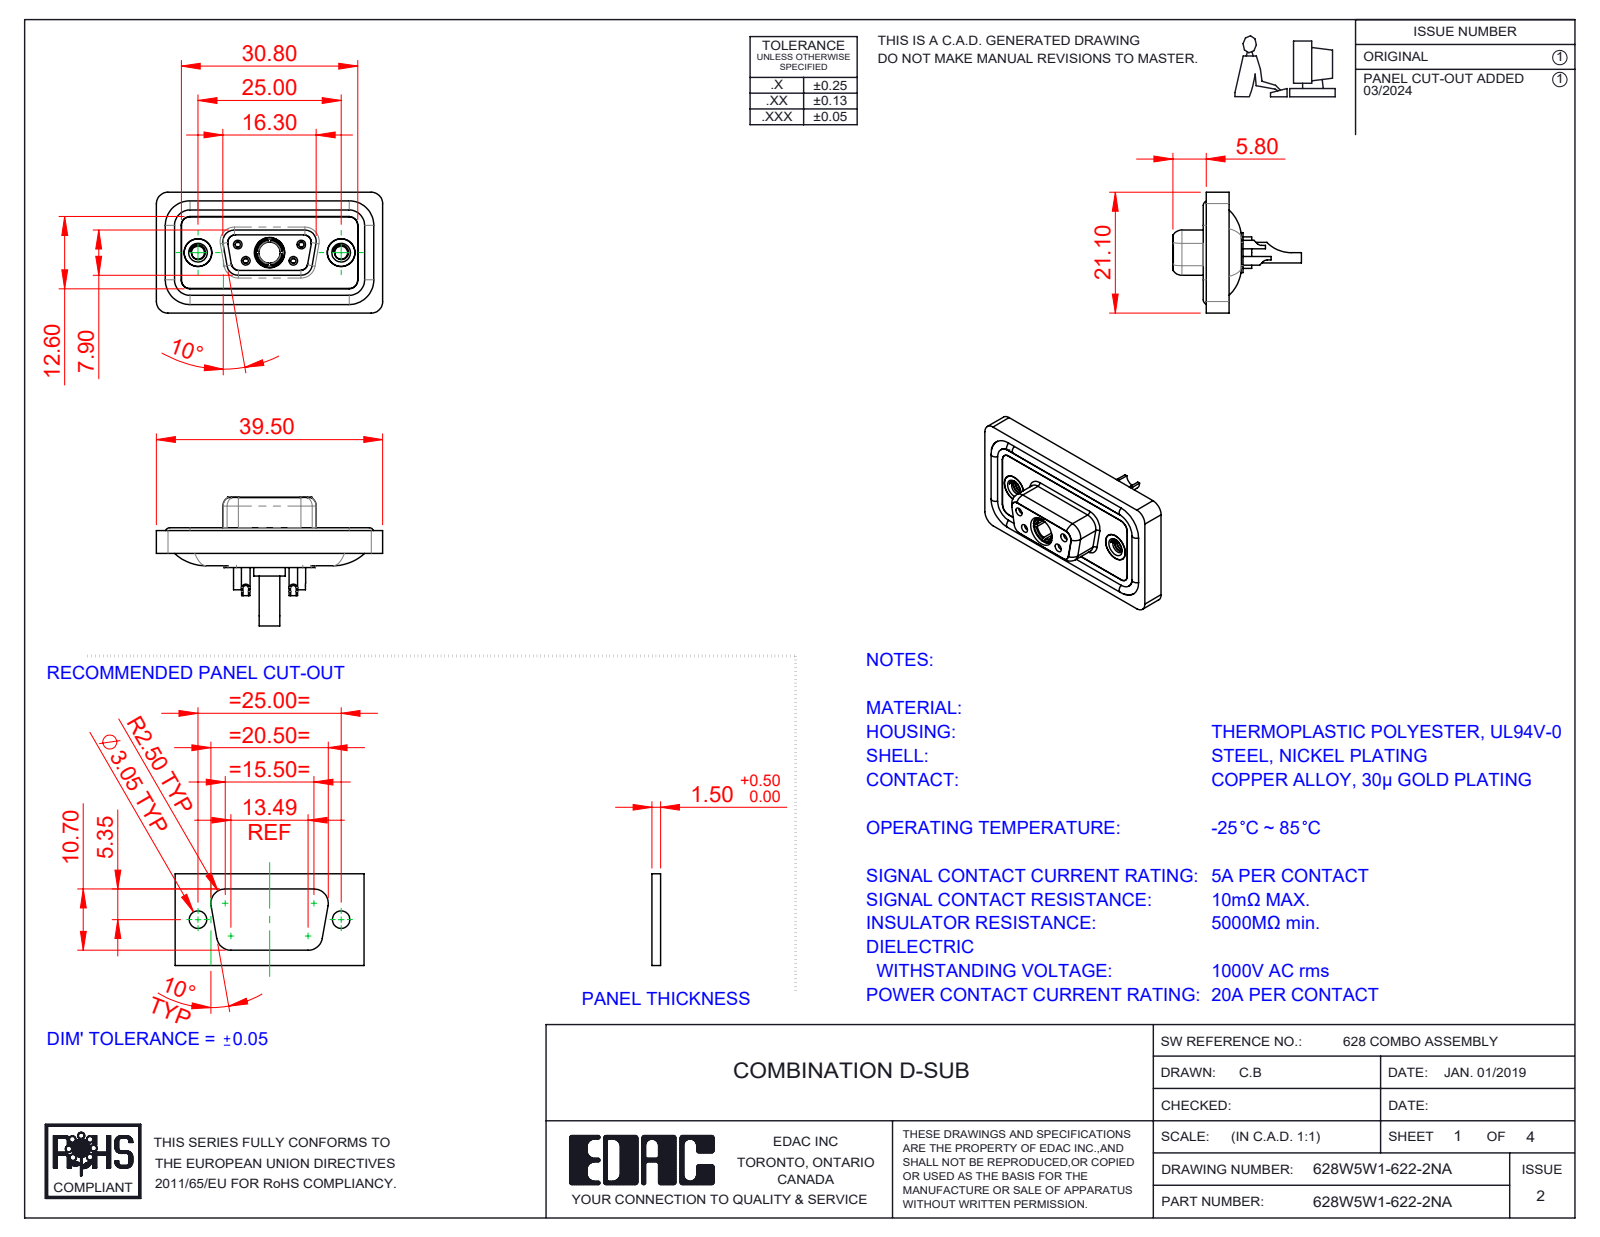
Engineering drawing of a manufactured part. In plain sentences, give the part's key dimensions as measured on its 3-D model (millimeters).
The part is named "628Combo Contact Row 1_22; 628Combo Threaded Rivet_A; Power Socket_20A SC; 628Combo Housing_5W1 (+5 more)". Its 3-D file was written by "SolidWorks 2023 (CONFIG_CONTROL_DESIGN)". It is 13 solids with 684 faces: 205 planar, 300 cylindrical and 179 other. Overall it measures 39.5 by 22.45 by 21.1 millimeters. Its volume is 4 789 cubic millimeters and its surface area 7 757 square millimeters. Round holes: 4 of diameter 0.9, 4 of diameter 1, 4 of diameter 1.1, 4 of diameter 1.5, 4 of diameter 2, 3 of diameter 4.85, 2 of diameter 1.6, 2 of diameter 1.7, 2 of diameter 2.26, 2 of diameter 4, 2 of diameter 4.05, 2 of diameter 5. Round bosses or shafts: 6 of diameter 1.6, 4 of diameter 2.2, 2 of diameter 4.95, 2 of diameter 4.8, 1 of diameter 5.5, 1 of diameter 5.2, 1 of diameter 4.96, 1 of diameter 4.75. Partial cylindrical surfaces (rounded edges, fillets, slot ends): 22 of radius 1.5, 18 of radius 2, 8 of radius 1.35, 8 of radius 1.6, 6 of radius 1, 4 of radius 0.25, 4 of radius 0.5, 4 of radius 0.6. The main face-to-face distances are 0.4, 2.9, 1.1, 1.8, 1.6, 0.5, 5.65, 7.45, 5.35, 3.6. The hole center spacings are 3.16, 5.72, 7.1, 12.5, 18.1, 4.39, 4.4, 8.31.
